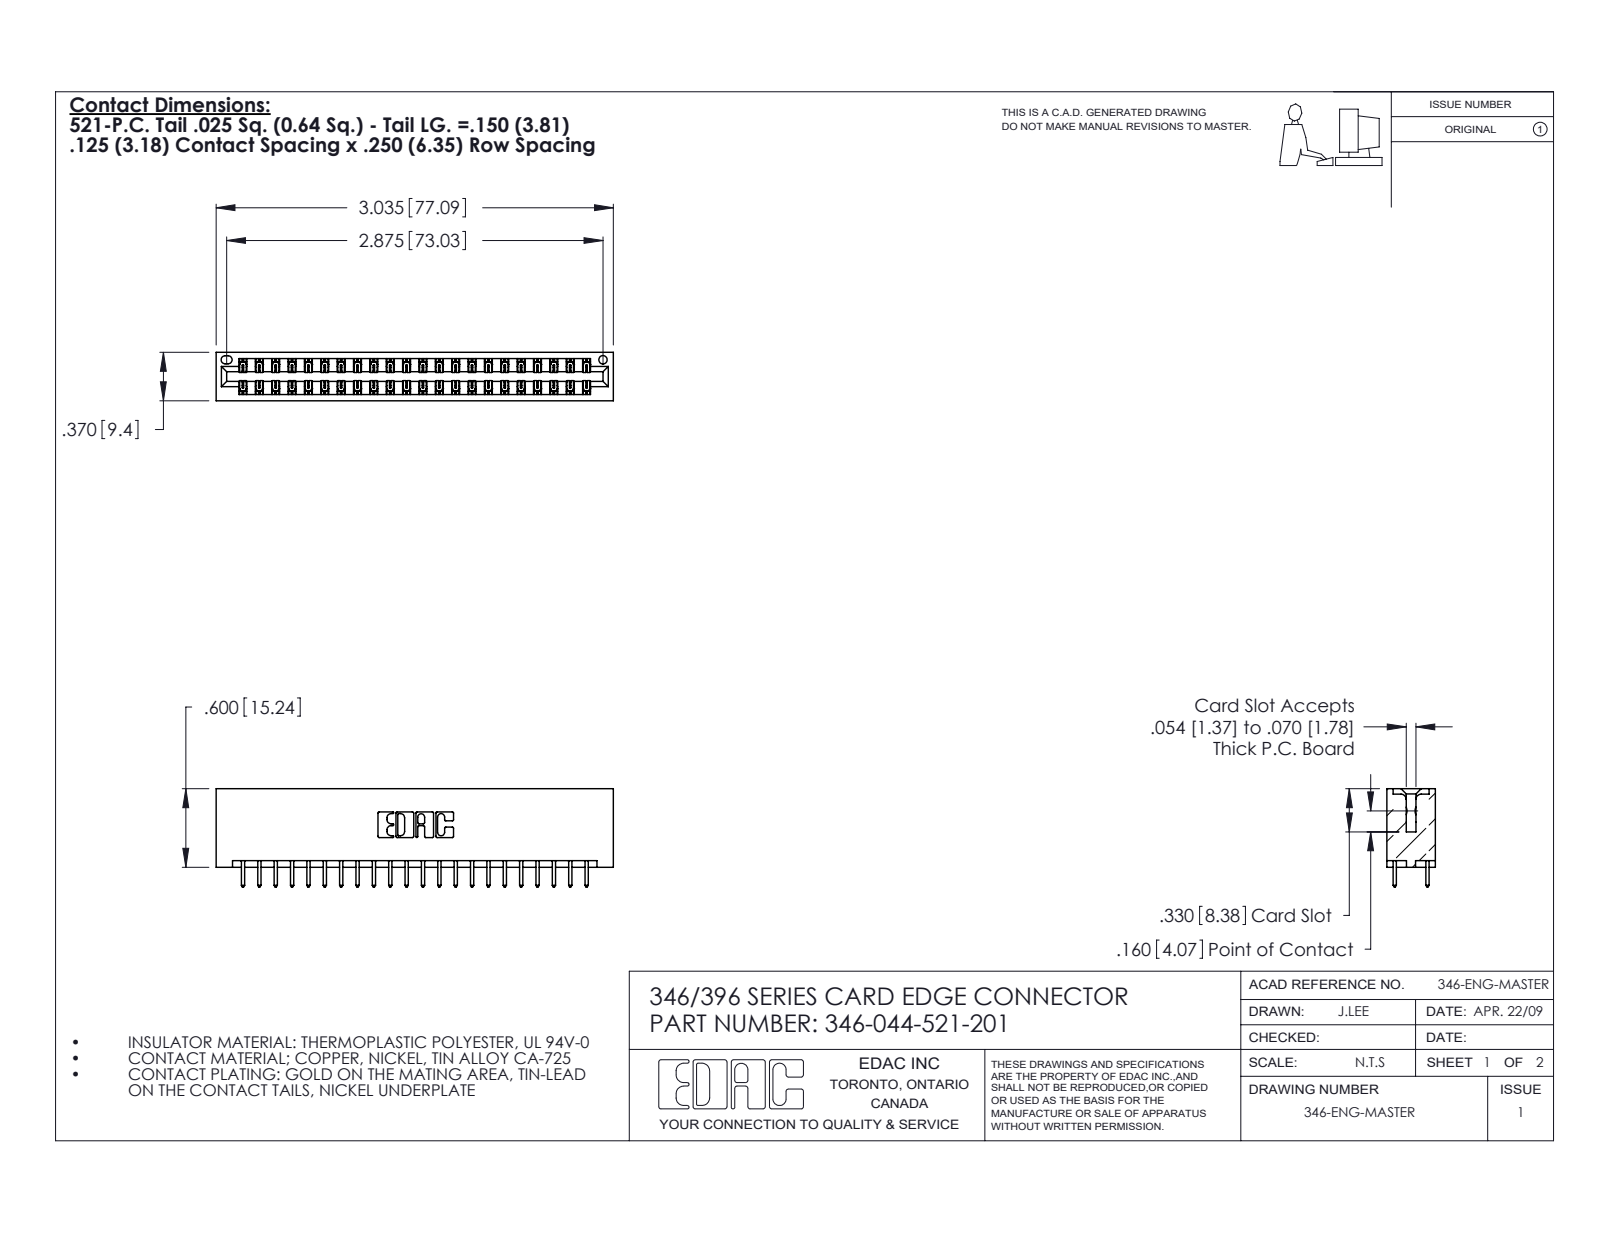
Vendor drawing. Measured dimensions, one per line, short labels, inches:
name: 346 Part_No Mounting Lugs; 346-044-521-201; 345-292-001_345-293-121
written by: SolidWorks 2020 (CONFIG_CONTROL_DESIGN)
unit: in
bodies: 45 solids, 2402 faces (1612 planar, 790 cylindrical, 0 other)
size: 3.035 × 0.75 × 0.37
volume: 0.483 in³; area: 16.45 in²
holes: 1× ⌀0.064
rounds: 66× R0.006, 44× R0.01, 22× R0.01, 6× R0.007, 6× R0.031, 3× R0.026, 2× R0.014, 2× R0.022
face distances: 0.048, 0.322, 0.25, 0.37, 0.072, 0.298, 0.025, 0.275, 0.148, 0.222
